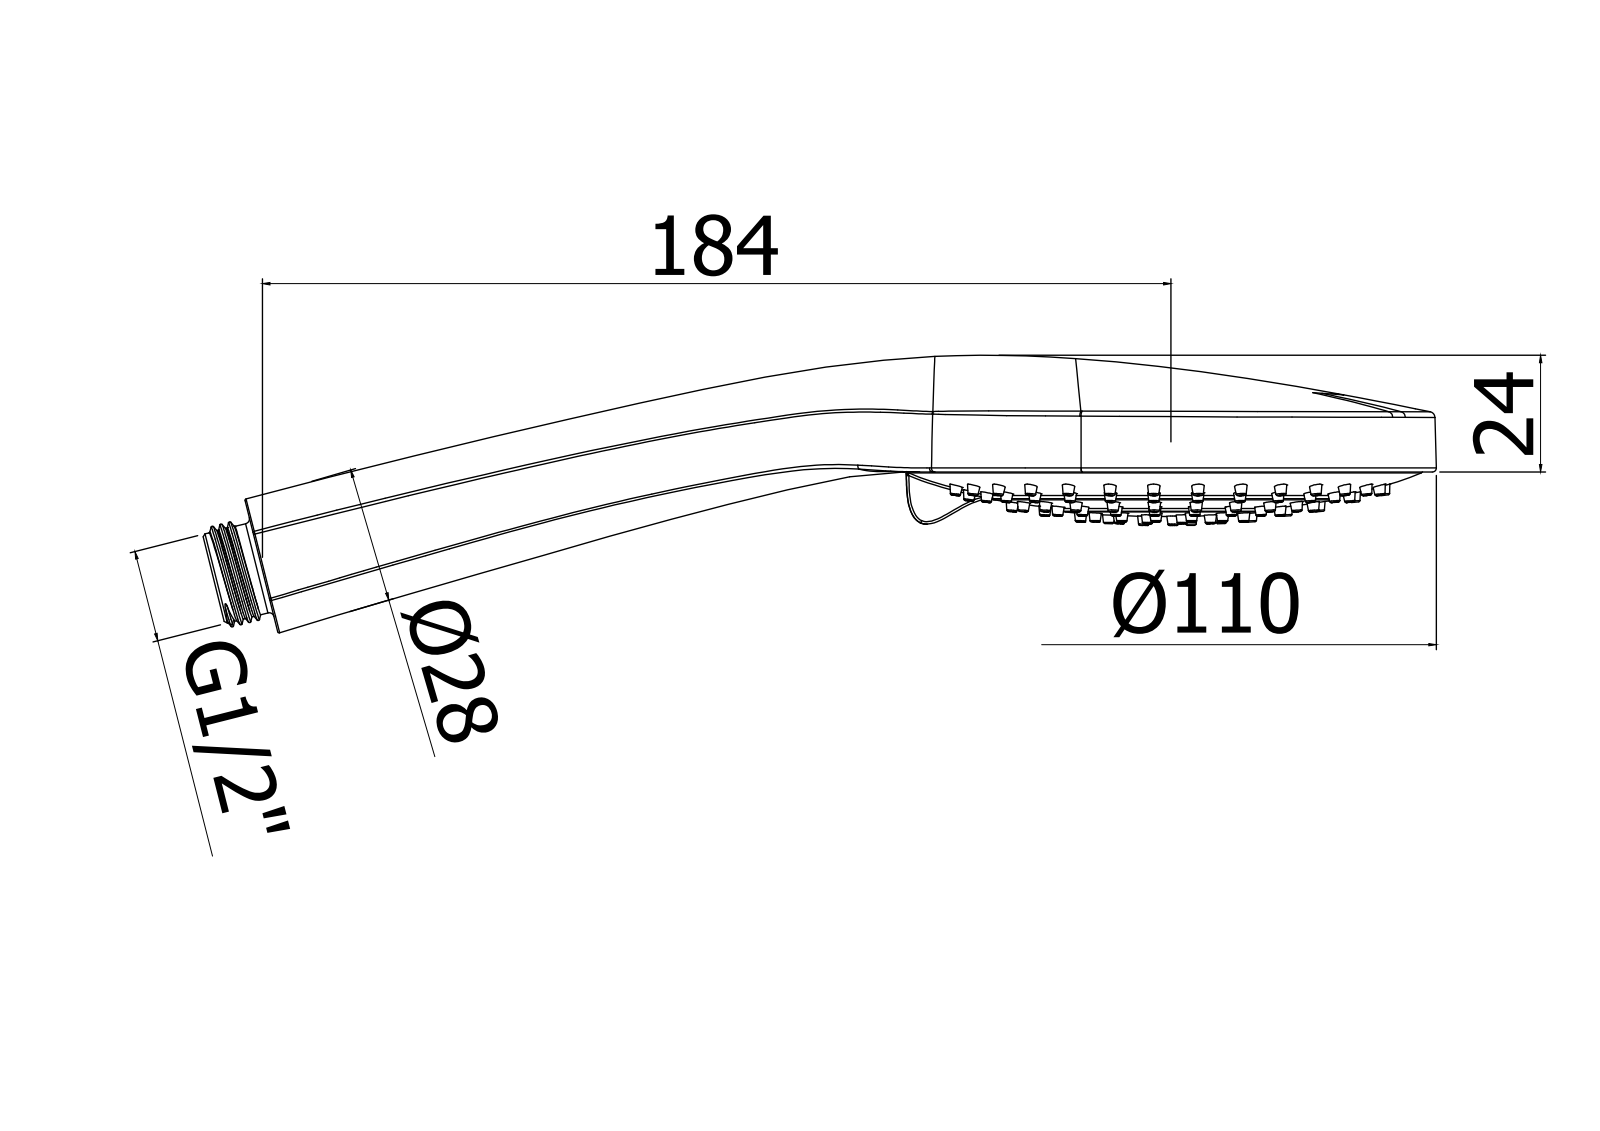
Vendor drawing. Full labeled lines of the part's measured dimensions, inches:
Part name (STEP PRODUCT): ZDOC125CR
STEP written by: CREO PARAMETRIC BY PTC INC, 2020044 (CONFIG_CONTROL_DESIGN)
Units: inches
Bodies: 2 solids, 3389 faces (647 planar, 586 cylindrical, 2156 other)
Overall size (bounding box): 9.835 × 4.329 × 2.215
Volume: 5.622 in³ · Surface area: 159.1 in²
Round holes (diameter × count): ⌀0.091 ×3, ⌀0.315 ×1, ⌀3.922 ×1
Round bosses / shafts (diameter × count): ⌀0.184 ×71, ⌀0.173 ×30, ⌀0.183 ×25, ⌀0.22 ×3, ⌀0.183 ×2, ⌀0.733 ×1, ⌀0.709 ×1
Partial cylindrical surfaces — rounded edges, fillets, slot ends (radius × count): R0.02 ×90, R0.039 ×64, R0.012 ×46, R0.031 ×37, R0.079 ×6, R0.118 ×4, R0.051 ×2, R1.472 ×2
Main face-to-face distances: 0.059, 0.734, 0.287, 0.256, 0.032, 0.201, 0.117, 0.079, 0.057, 0.142
Hole centre spacings: 0.896, 1.122, 0.551, 1.772
